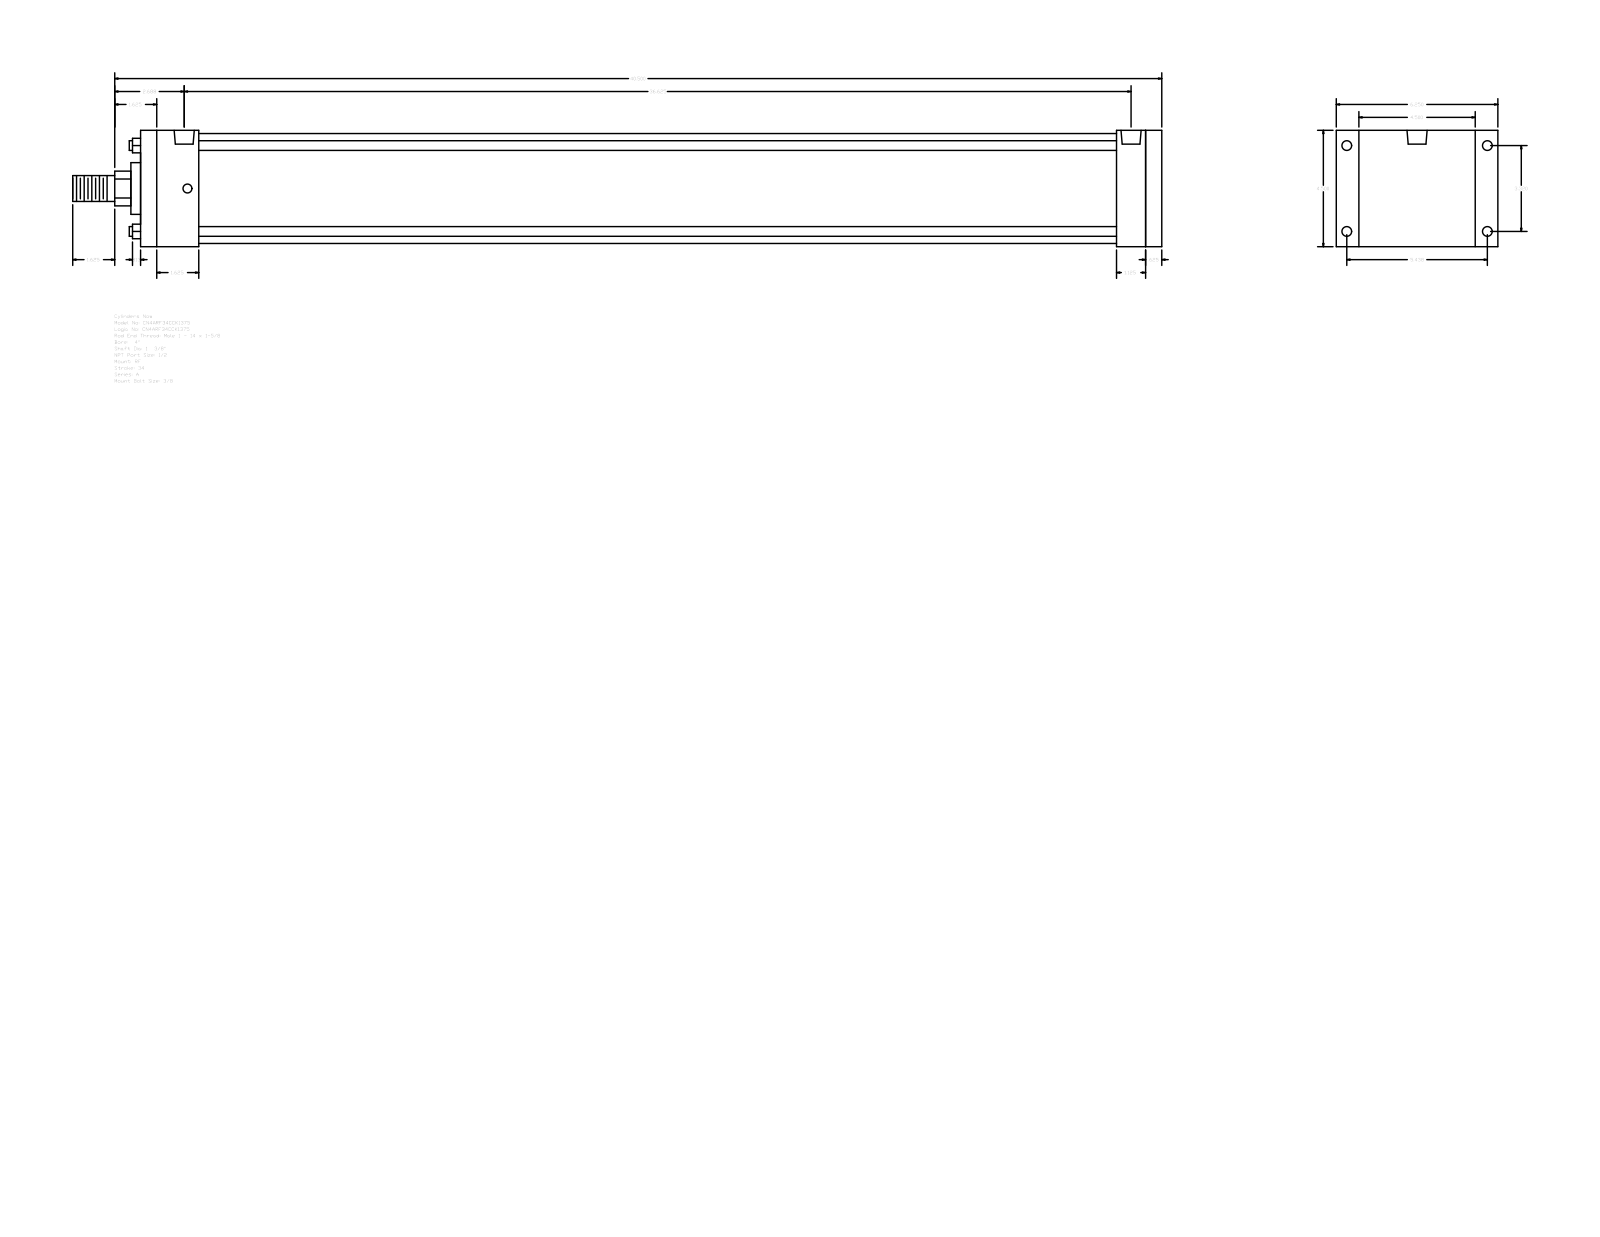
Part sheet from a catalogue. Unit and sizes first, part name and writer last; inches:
Units: inches
Overall size (bounding box): 42.125 × 6.25 × 4.5
Round holes (diameter × count): ⌀0.344 ×4, ⌀0.375 ×4, ⌀0.778 ×2
Round bosses / shafts (diameter × count): ⌀0.375 ×4, ⌀4.25 ×1, ⌀2 ×1, ⌀1.375 ×1, ⌀1 ×1
Partial cylindrical surfaces — rounded edges, fillets, slot ends (radius × count): R0.672 ×1
Main face-to-face distances: 4.5, 39.5, 38.875, 0.625, 2.25, 1.125, 0.875, 5.375, 37.75, 1.75
Hole centre spacings: 0.125, 3.32, 5.438, 6.371, 36.375, 36.5, 36.625
Bodies: 0 solids, 92 faces (64 planar, 28 cylindrical, 0 other)
Part name (STEP PRODUCT): A_RF__0400_1.375
STEP written by: GSSL Pune (CONFIG_CONTROL_DESIGN)
